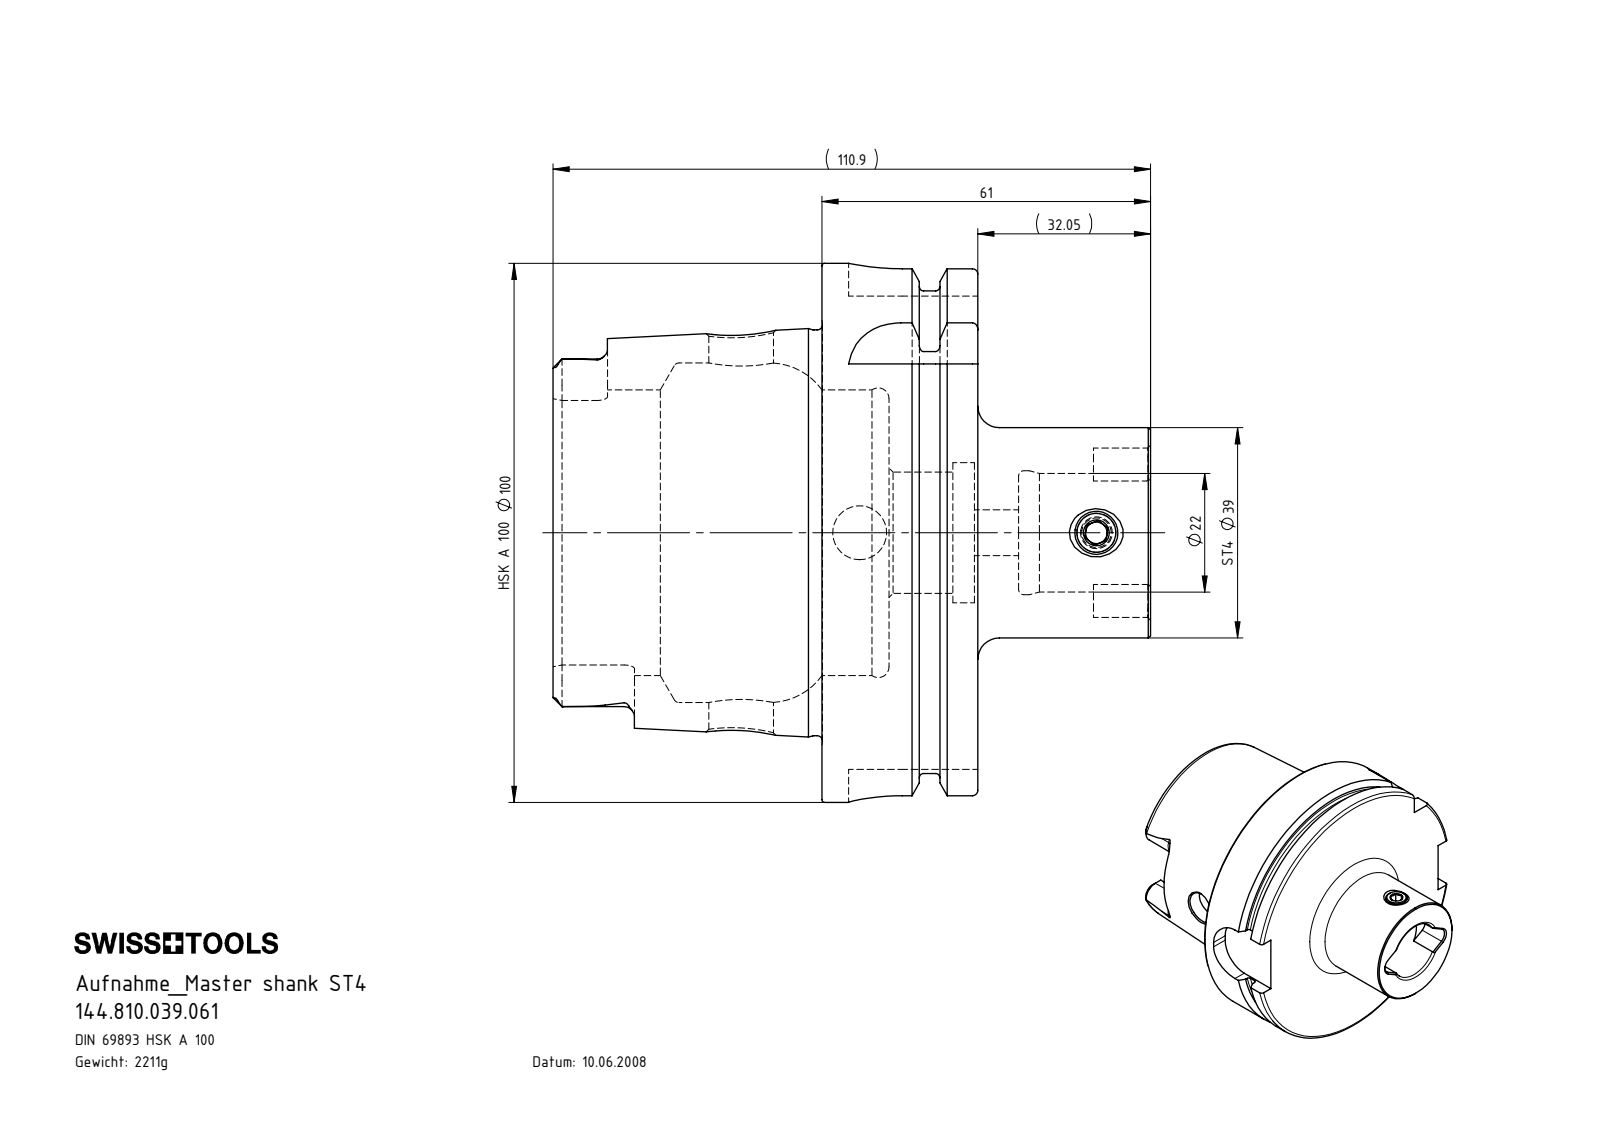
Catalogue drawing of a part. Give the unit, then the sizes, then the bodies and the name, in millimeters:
Units: millimetres
Overall size (bounding box): 110.9 × 100 × 100
Round holes (diameter × count): ⌀4 ×1, ⌀7.25 ×1, ⌀8.5 ×1, ⌀10 ×1, ⌀12 ×1, ⌀22 ×1, ⌀22.5 ×1, ⌀23 ×1, ⌀26 ×1, ⌀53 ×1, ⌀63 ×1
Round bosses / shafts (diameter × count): ⌀100 ×1, ⌀91.95 ×1, ⌀75.26 ×1, ⌀39 ×1, ⌀8 ×1
Partial cylindrical surfaces — rounded edges, fillets, slot ends (radius × count): R1.9 ×6, R4.88 ×4, R10 ×4, R3.2 ×2
Main face-to-face distances: 28.95, 12.45, 16.5, 49.9, 62.35, 78.85, 110.9, 61, 48.55, 32.05
Hole centre spacings: 43.95
Volume: 281 541 mm³ · Surface area: 55 744 mm²
Bodies: 2 solids, 158 faces (63 planar, 39 cylindrical, 56 other)
Part name (STEP PRODUCT): HA0-ST4.K01.061_B_Fertigbearbeitung; ST4-ER1.001.011_A; HA0.ST4.K01.061
STEP written by: SolidWorks 2017 (AUTOMOTIVE_DESIGN)
